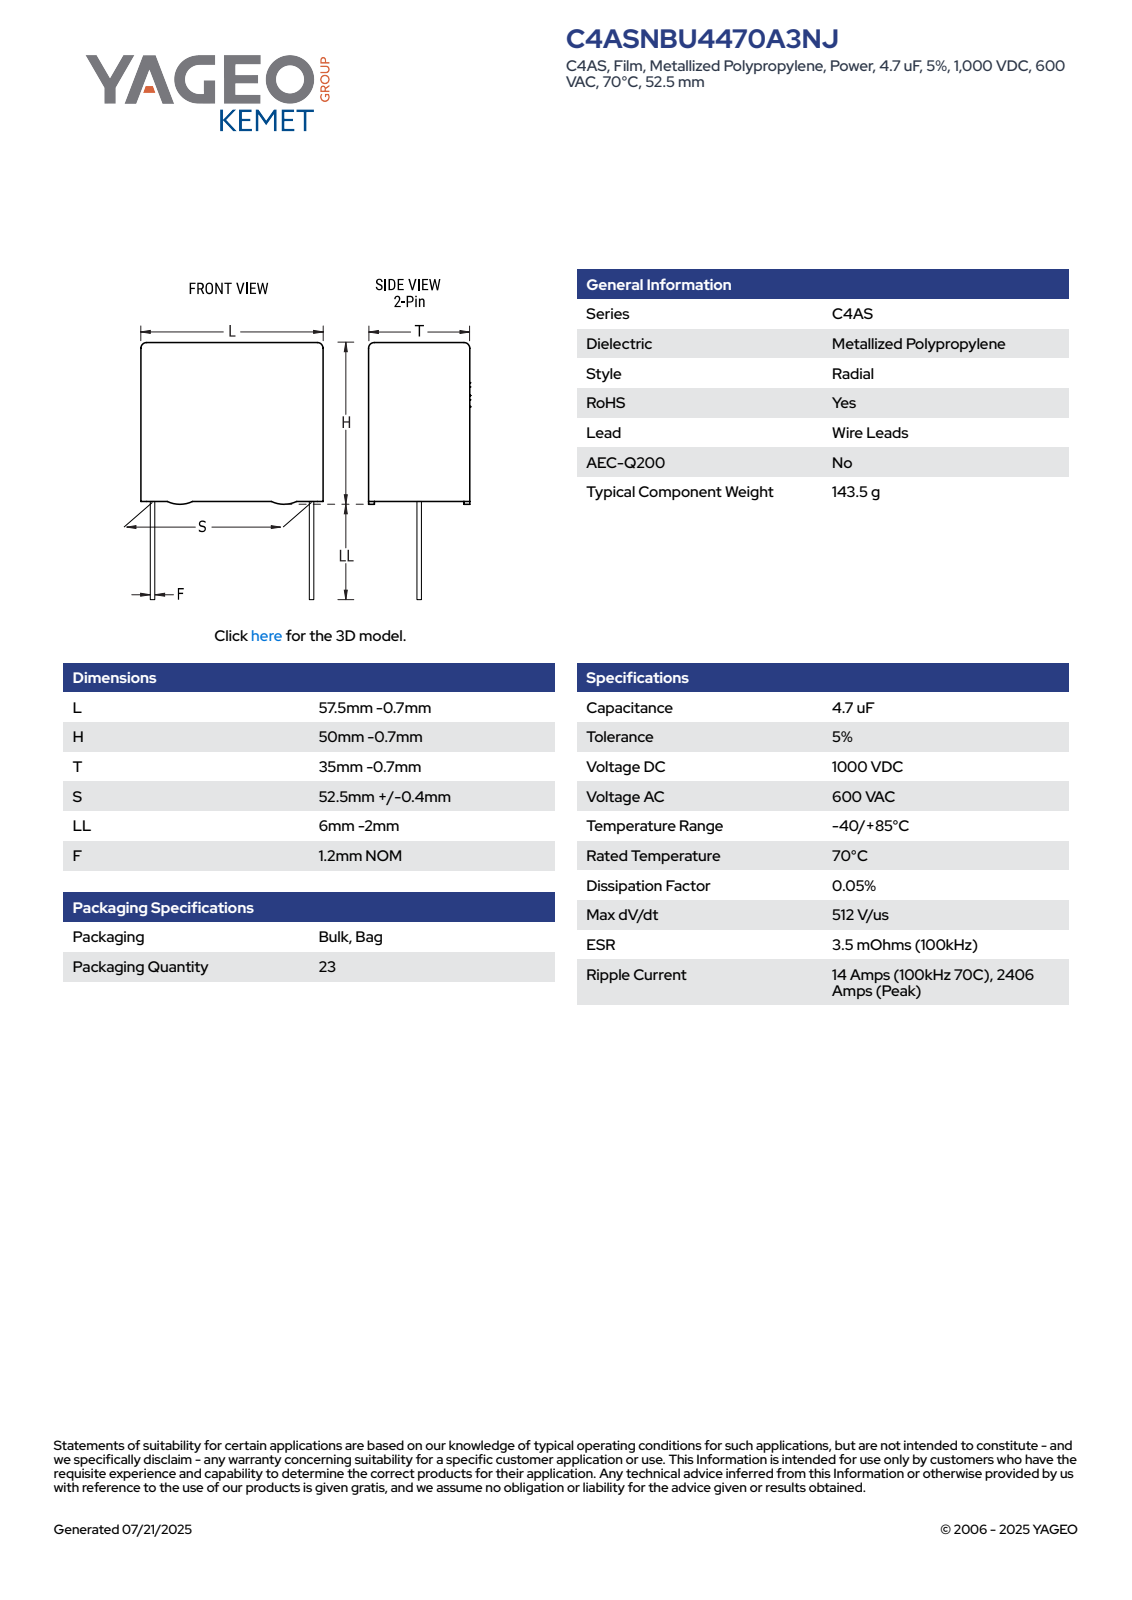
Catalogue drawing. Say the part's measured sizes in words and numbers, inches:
The part is named "CFP_RB_57.5X50X35_L56.8H49.3T34.3S52.5LL4F1.2". Its 3-D file was written by "SolidWorks 2014 (AUTOMOTIVE_DESIGN)". It is 4 solids with 89 faces: 81 planar, 8 cylindrical and 0 other. Overall it measures 2.236 by 2.098 by 1.35 inches. Its volume is 5.748 cubic inches and its surface area 20.03 square inches. Round bosses or shafts: 2 of diameter 0.047. Partial cylindrical surfaces (rounded edges, fillets, slot ends): 4 of radius 0.02. The main face-to-face distances are 1.35, 1.902, 2.236, 0.039, 1.941, 0.077, 1.273, 1.196, 1.61, 1.61.
